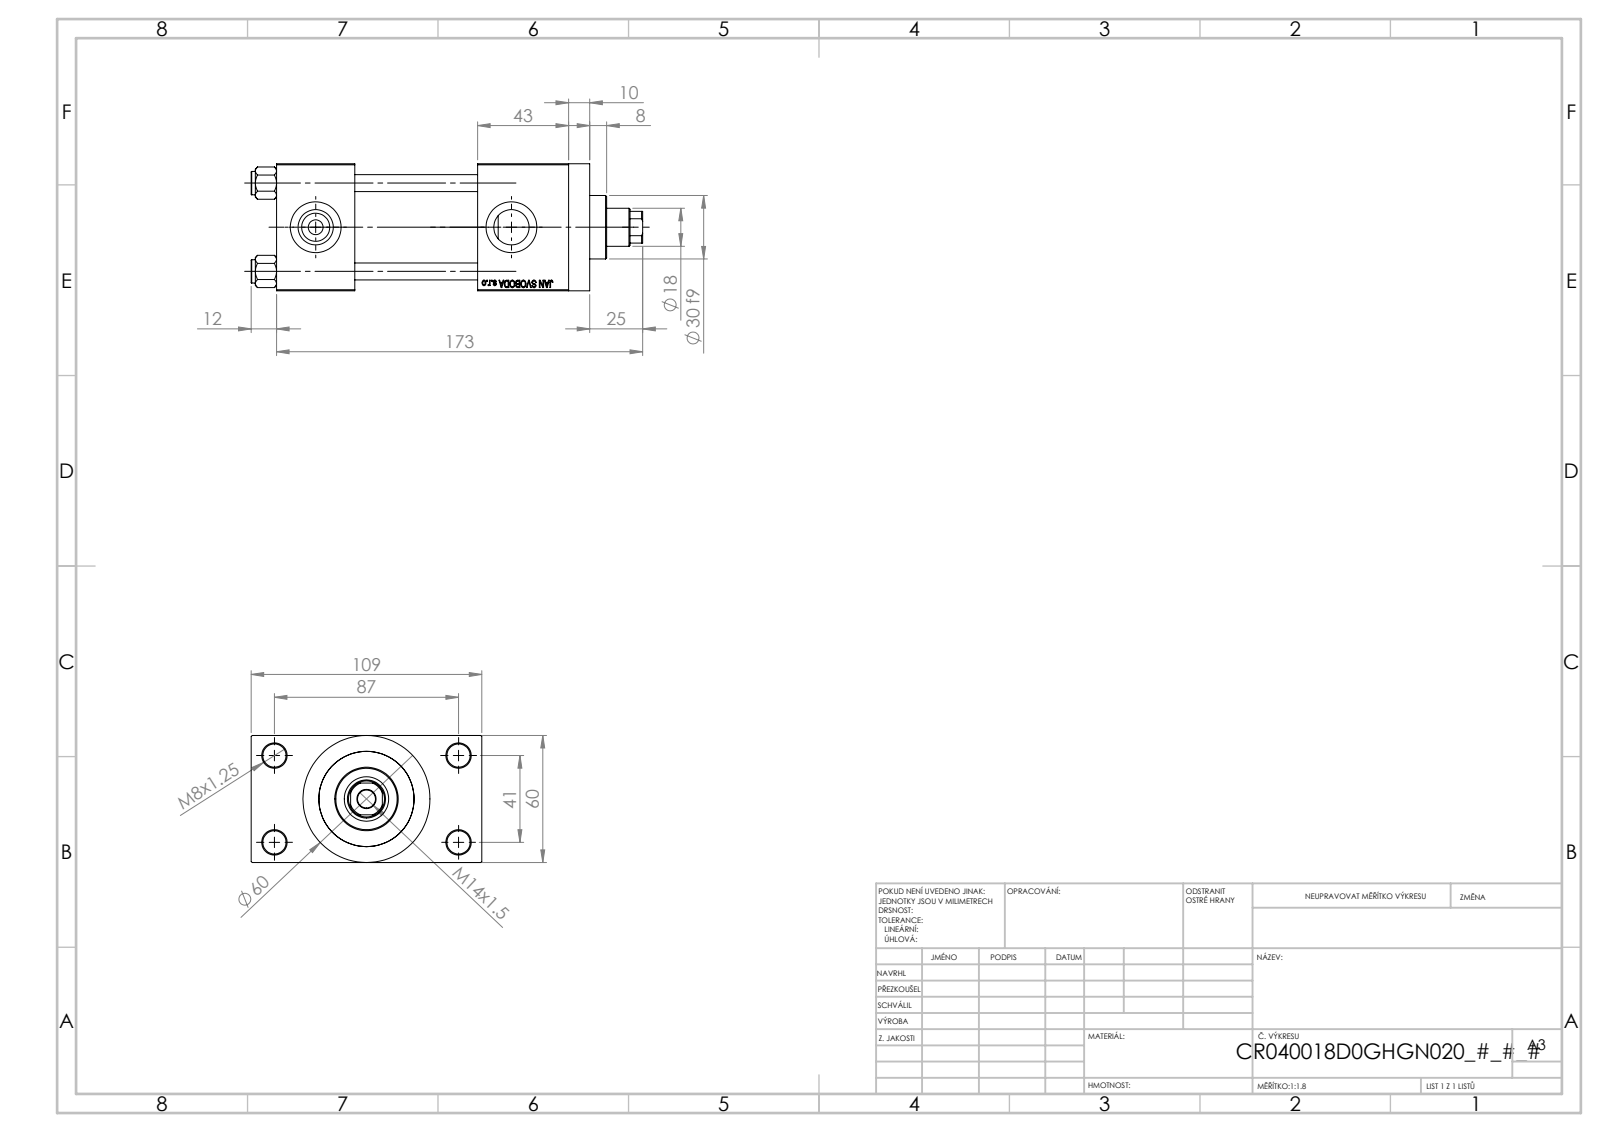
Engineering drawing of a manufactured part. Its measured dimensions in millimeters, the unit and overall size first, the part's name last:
Units: millimetres
Overall size (bounding box): 185 × 109 × 60
Round holes (diameter × count): ⌀8 ×4, ⌀11 ×4, ⌀7 ×2, ⌀16.66 ×2, ⌀24 ×2, ⌀8.5 ×1, ⌀18 ×1, ⌀21 ×1, ⌀31 ×1, ⌀40 ×1, ⌀45 ×1
Round bosses / shafts (diameter × count): ⌀11 ×4, ⌀60 ×1, ⌀46 ×1, ⌀30 ×1
Partial cylindrical surfaces — rounded edges, fillets, slot ends (radius × count): R8.5 ×1
Main face-to-face distances: 60, 58, 24.5, 84.5, 37, 95, 138, 101, 43, 10
Hole centre spacings: 22.65, 29.49, 41.7, 47.15, 48.09, 64.35, 76.49, 41
Volume: 512 522 mm³ · Surface area: 122 547 mm²
Bodies: 11 solids, 1104 faces (498 planar, 88 cylindrical, 518 other)
Part name (STEP PRODUCT): V215CR_D_Body; V215CR_D_TYCINKA; NUT_M5_D; V215CR_VCP_D (+1 more)
STEP written by: SolidWorks 2019 (CONFIG_CONTROL_DESIGN)
